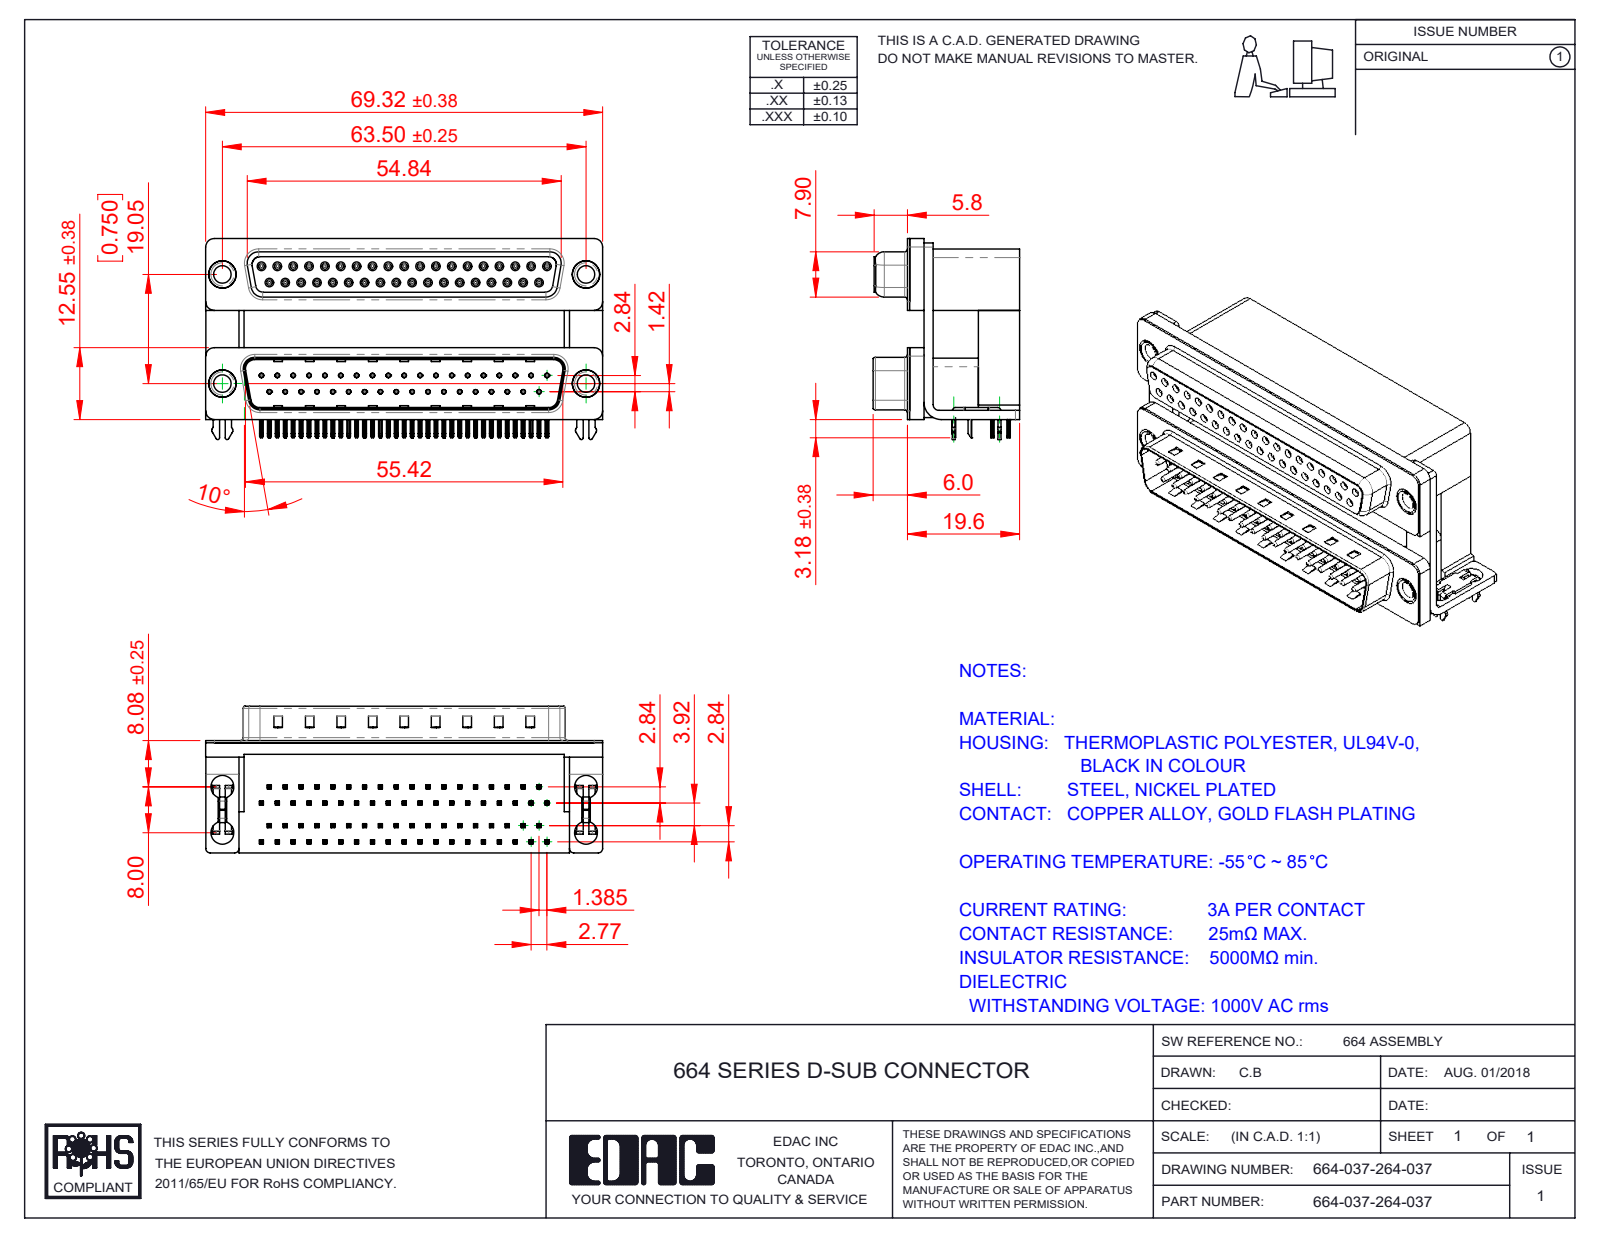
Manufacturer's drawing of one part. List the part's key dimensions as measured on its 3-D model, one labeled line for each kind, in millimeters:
Part name (STEP PRODUCT): 664 Contact Top Upper_M; 664-037-264-037; 664 Mounting Bracket_2ProngM; 664 Contact Top Lower (+8 more)
STEP written by: SolidWorks 2020 (CONFIG_CONTROL_DESIGN)
Units: millimetres
Bodies: 87 solids, 9013 faces (4843 planar, 2191 cylindrical, 1979 other)
Overall size (bounding box): 69.32 × 35.1 × 25.6
Volume: 31 087 mm³ · Surface area: 32 846 mm²
Round holes (diameter × count): ⌀0.8 ×74, ⌀0.35 ×37, ⌀0.9 ×37, ⌀4 ×8, ⌀3.05 ×4, ⌀3.5 ×4, ⌀4.8 ×4, ⌀5 ×4
Round bosses / shafts (diameter × count): ⌀1.2 ×37, ⌀0.75 ×37, ⌀4.9 ×4, ⌀4.75 ×4, ⌀3.85 ×4
Partial cylindrical surfaces — rounded edges, fillets, slot ends (radius × count): R0.1 ×298, R0.25 ×158, R0.15 ×148, R0.12 ×74, R0.35 ×74, R0.34 ×37, R0.28 ×18, R0.5 ×16
Main face-to-face distances: 0.4, 19.2, 7.2, 12, 10.69, 2.19, 2.84, 18.7, 29.39, 19.05
Hole centre spacings: 2.77, 5.54, 3.16, 8.31, 11.08, 13.85, 16.62, 19.39
